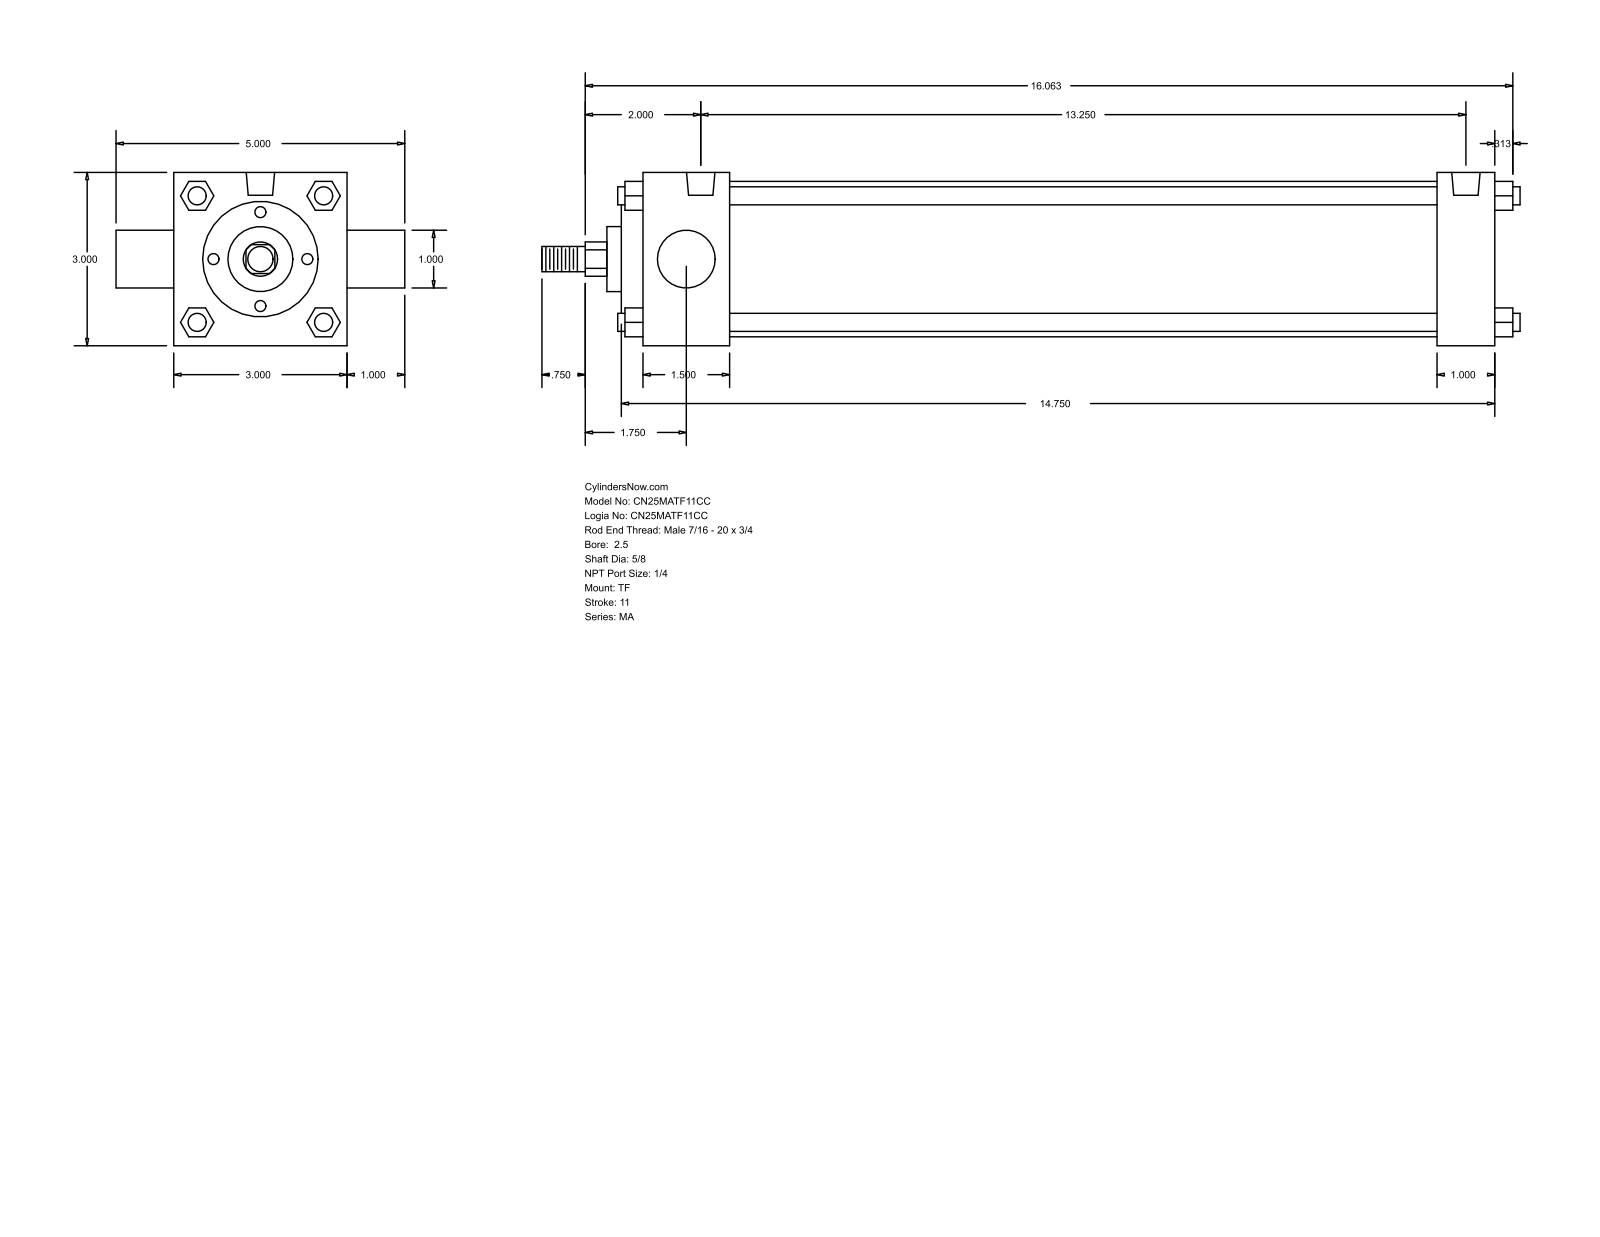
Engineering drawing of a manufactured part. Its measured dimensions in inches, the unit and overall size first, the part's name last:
Units: inches
Overall size (bounding box): 16.937 × 5 × 3
Round holes (diameter × count): ⌀0.313 ×3, ⌀0.492 ×2
Round bosses / shafts (diameter × count): ⌀0.313 ×4, ⌀2.69 ×1, ⌀2 ×1, ⌀1.125 ×1, ⌀1 ×1, ⌀0.625 ×1, ⌀0.437 ×1
Partial cylindrical surfaces — rounded edges, fillets, slot ends (radius × count): R0.297 ×1
Main face-to-face distances: 3, 14.75, 1, 1.5, 13.75, 12.25, 13.25, 0.5, 0.375, 1.875
Hole centre spacings: 13.25
Bodies: 0 solids, 122 faces (93 planar, 29 cylindrical, 0 other)
Part name (STEP PRODUCT): MA_TF__0250_0.625
STEP written by: GSSL Pune (CONFIG_CONTROL_DESIGN)
